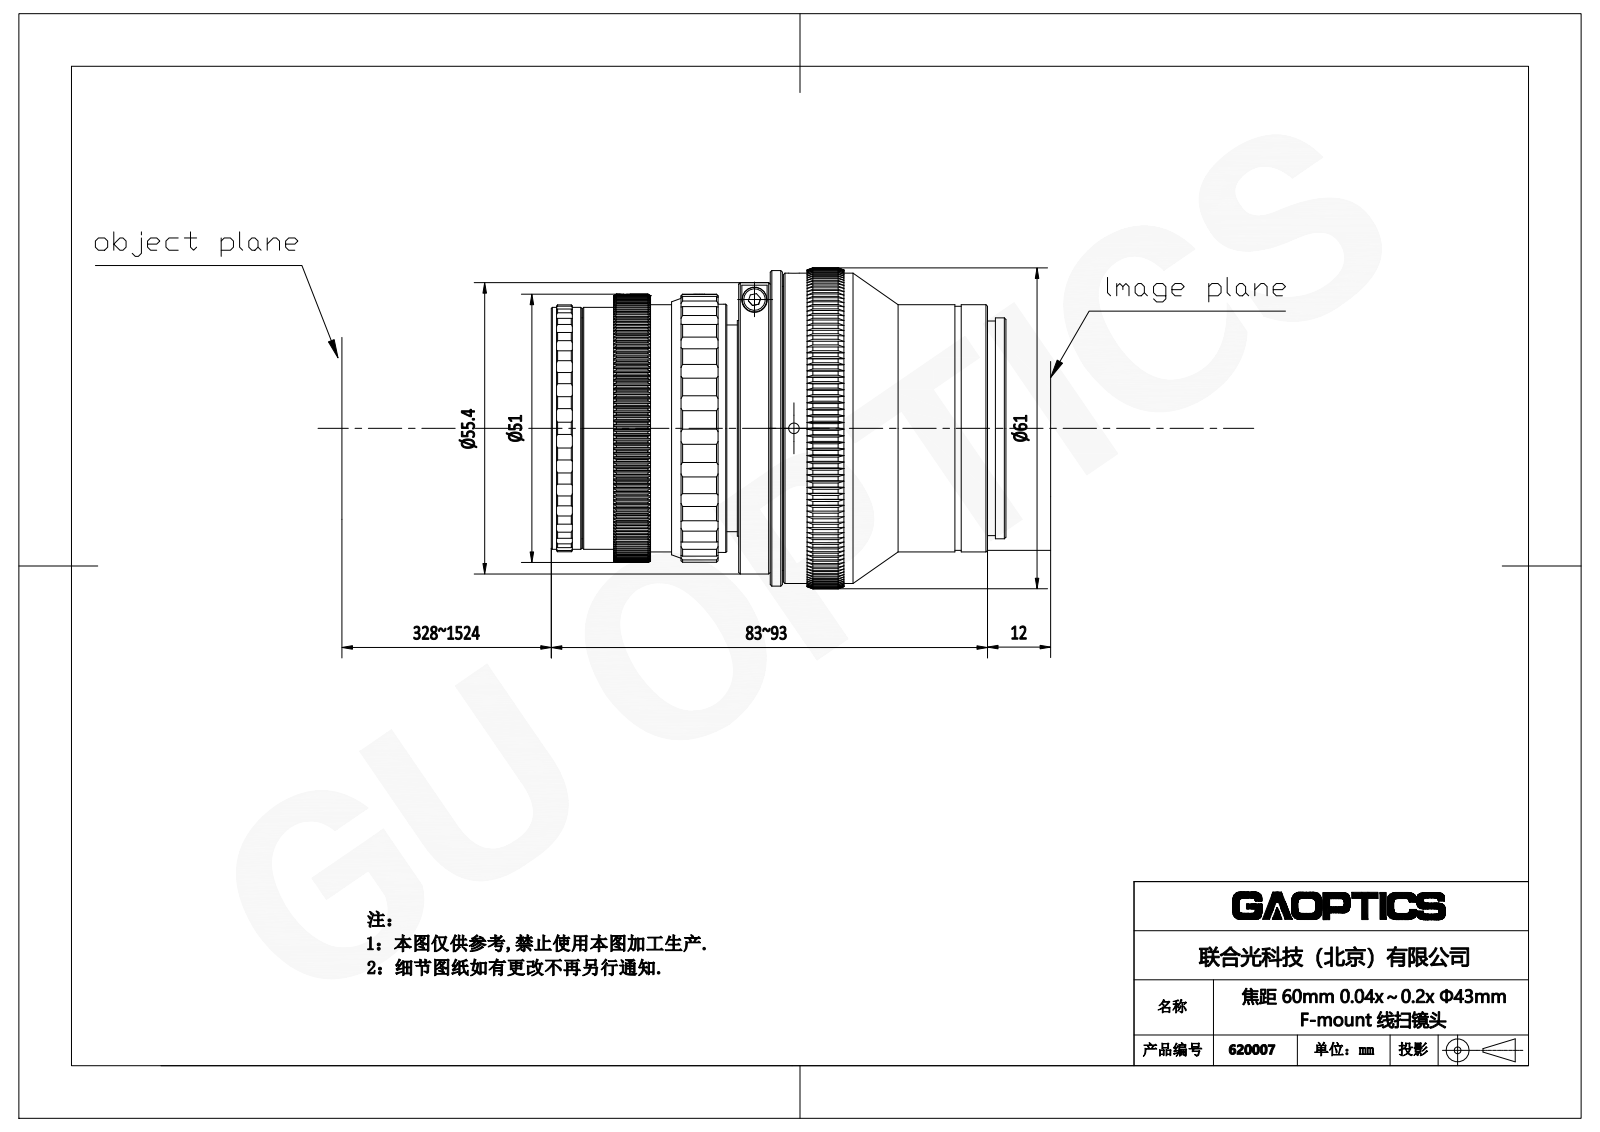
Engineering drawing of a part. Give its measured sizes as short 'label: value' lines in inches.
name: E1; M2.5x5 平头顶丝; E2; 前镜筒 (+3 more)
written by: SolidWorks 2016 (AUTOMOTIVE_DESIGN)
unit: in
bodies: 21 solids, 2922 faces (940 planar, 1002 cylindrical, 980 other)
size: 3.403 × 2.402 × 2.402
volume: 5.98 in³; area: 115.7 in²
holes: 5× ⌀0.079, 2× ⌀0.051, 1× ⌀0.055, 1× ⌀0.102, 1× ⌀0.433, 1× ⌀0.504, 1× ⌀0.637, 1× ⌀0.709, 1× ⌀0.827, 1× ⌀0.835, 1× ⌀0.945, 1× ⌀1
bosses: 2× ⌀0.098, 2× ⌀0.079, 1× ⌀2.362, 1× ⌀2.323, 1× ⌀2.181, 1× ⌀2.126, 1× ⌀2.047, 1× ⌀1.858
rounds: 180× R0.006, 55× R0.098, 7× R0.039, 4× R0.197, 2× R0.049, 1× R0.03, 1× R0.069, 1× R0.094
face distances: 0.177, 0.236, 0.504, 0.268, 0.691, 0.424, 0.098, 0.836, 1.072, 1.34
hole spacings: 0.65, 0.157, 0.552, 0.553, 0.709, 0.711, 1.262, 1.299
